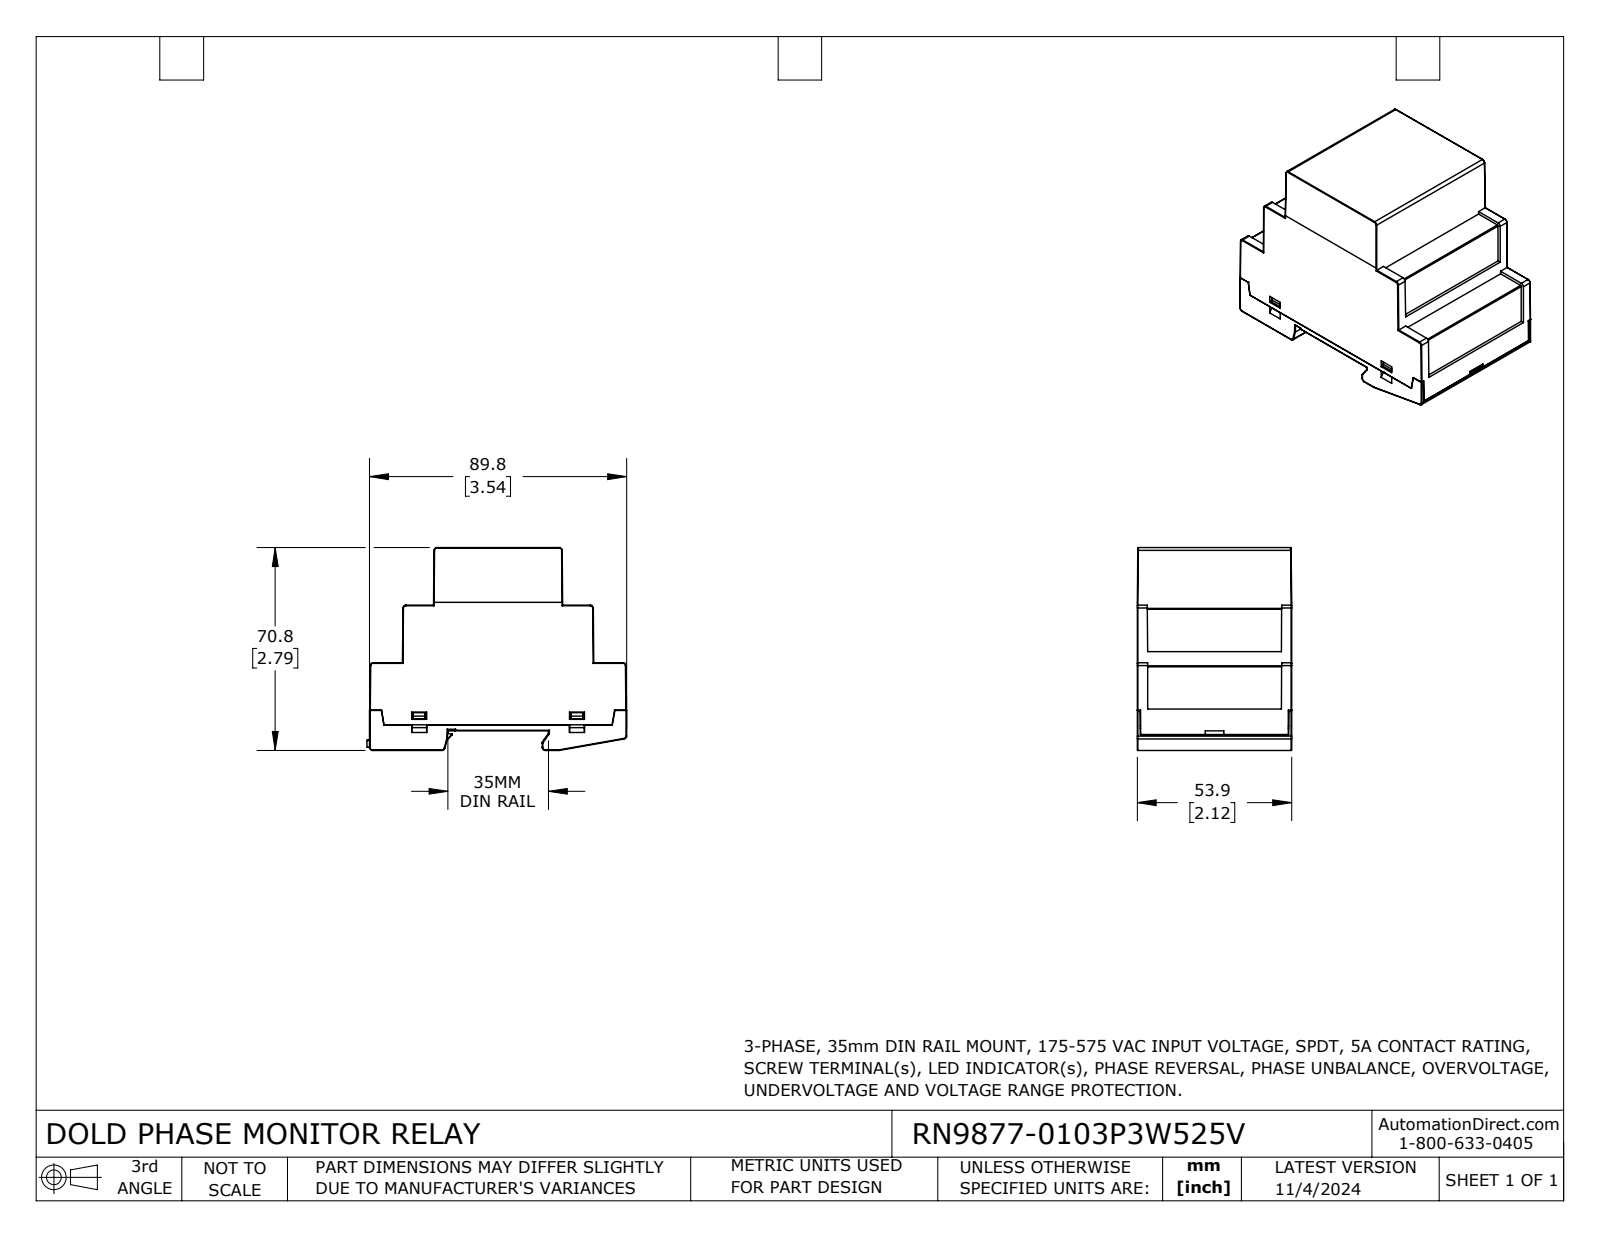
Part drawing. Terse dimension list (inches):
name: RN9877-0103P3W525V
written by: SolidWorks 2023 (CONFIG_CONTROL_DESIGN)
unit: in
bodies: 3 solids, 1027 faces (823 planar, 126 cylindrical, 78 other)
size: 3.572 × 2.787 × 2.122
volume: 13.92 in³; area: 70.57 in²
bosses: 5× ⌀0.098, 1× ⌀0.181
rounds: 44× R0.008, 18× R0.039, 11× R0.02, 9× R0.004, 4× R0.012, 2× R0.016, 1× R0.011, 1× R0.028
face distances: 2.122, 2.435, 0.041, 0.085, 2.52, 0.217, 0.352, 0.26, 0.175, 2.26
